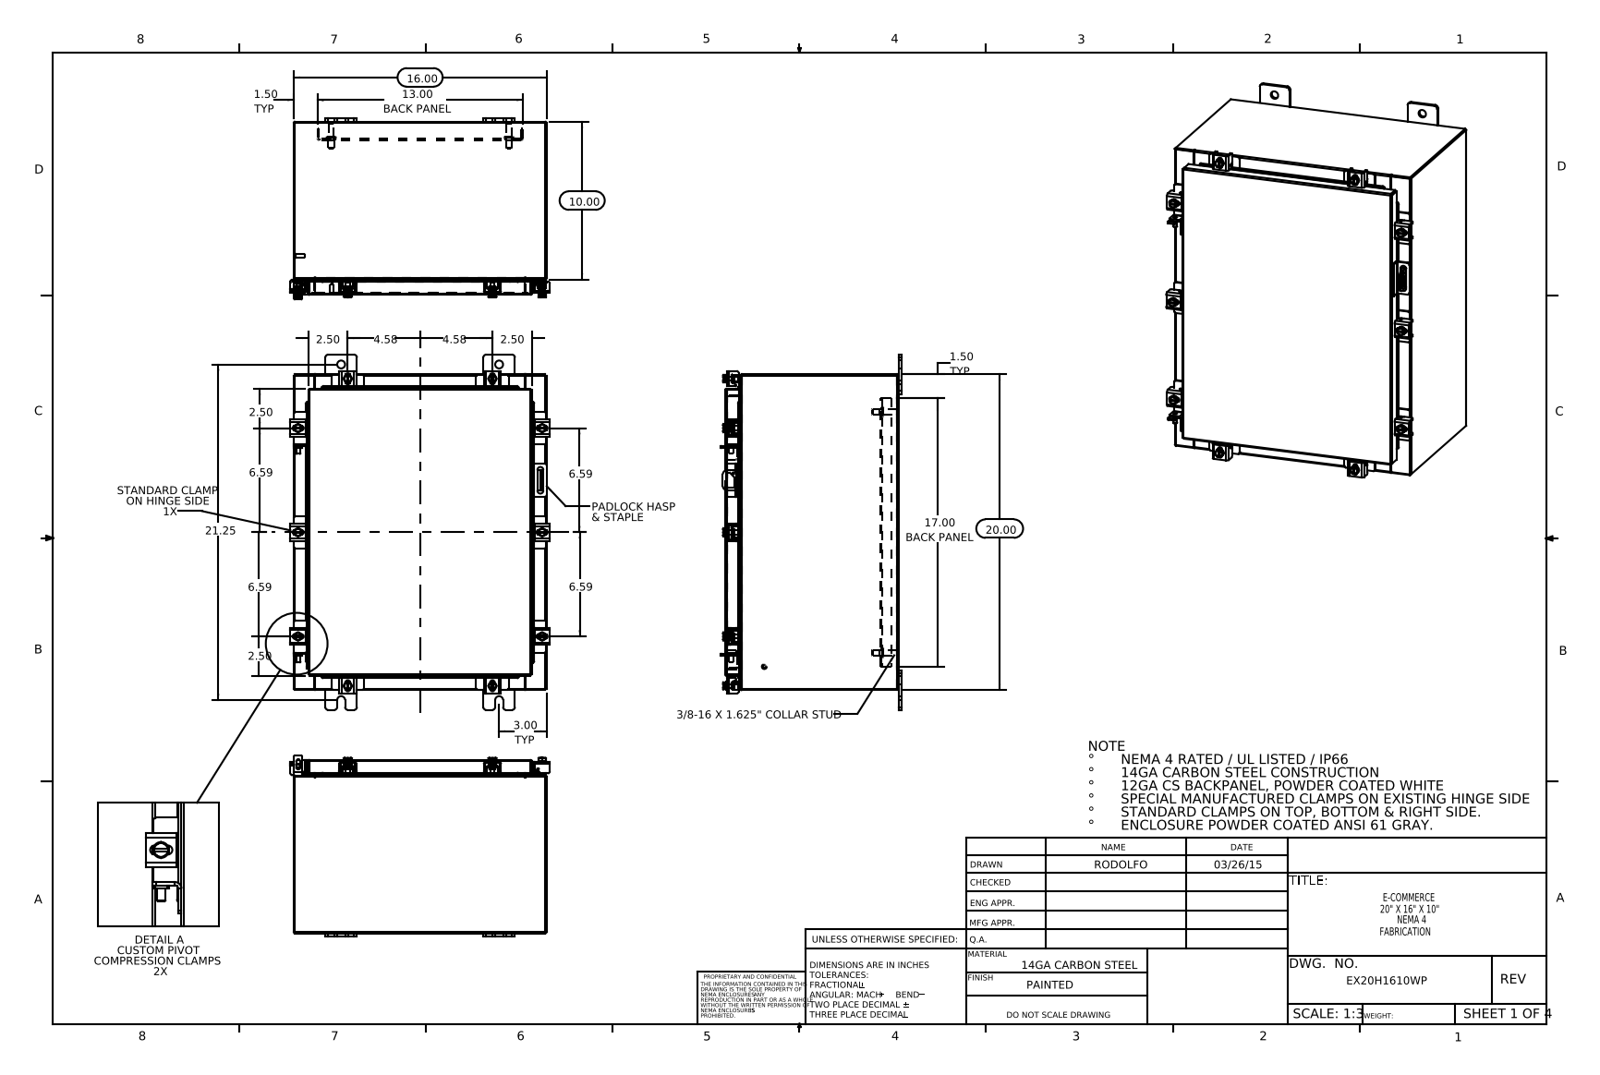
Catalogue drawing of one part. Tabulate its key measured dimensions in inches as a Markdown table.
| quantity | value |
| --- | --- |
| part name | 30X10 Clamp Bracket2; EX20H1610WP; N-WMT04X30402202210-00 22101002; N-WMT04X30402202210-00 22104005_DEFAULT (+8 more) |
| STEP written by | SolidWorks 2014 (CONFIG_CONTROL_DESIGN) |
| units | inches |
| bodies | 71 solids, 1784 faces (955 planar, 685 cylindrical, 144 other) |
| overall size | 22.5 × 16.421 × 11.453 |
| volume | 146.1 in³ |
| surface area | 3 692 in² |
| round holes (diameter × count) | 0.213 × 10, 0.26 × 10, 0.5 × 8, 0.125 × 1, 0.25 × 1 |
| round bosses / shafts (diameter × count) | 0.5 × 10, 0.25 × 10, 0.399 × 8, 0.625 × 4, 0.375 × 4, 0.33 × 4, 0.315 × 2, 0.236 × 2 |
| partial cylindrical surfaces (radius × count) | 0.06 × 46, 0.013 × 24, 0.19 × 24, 0.088 × 22, 0.141 × 20, 0.12 × 18, 0.09 × 16, 0.1 × 16 |
| main face-to-face distances | 0.075, 10.9, 15.925, 19.925, 10.975, 10.826, 0.104, 1, 1.075, 9.826 |
| hole center spacings | 2.347, 4.44, 6.594, 10.222, 12.696, 14.374, 15.683, 16.62 |
